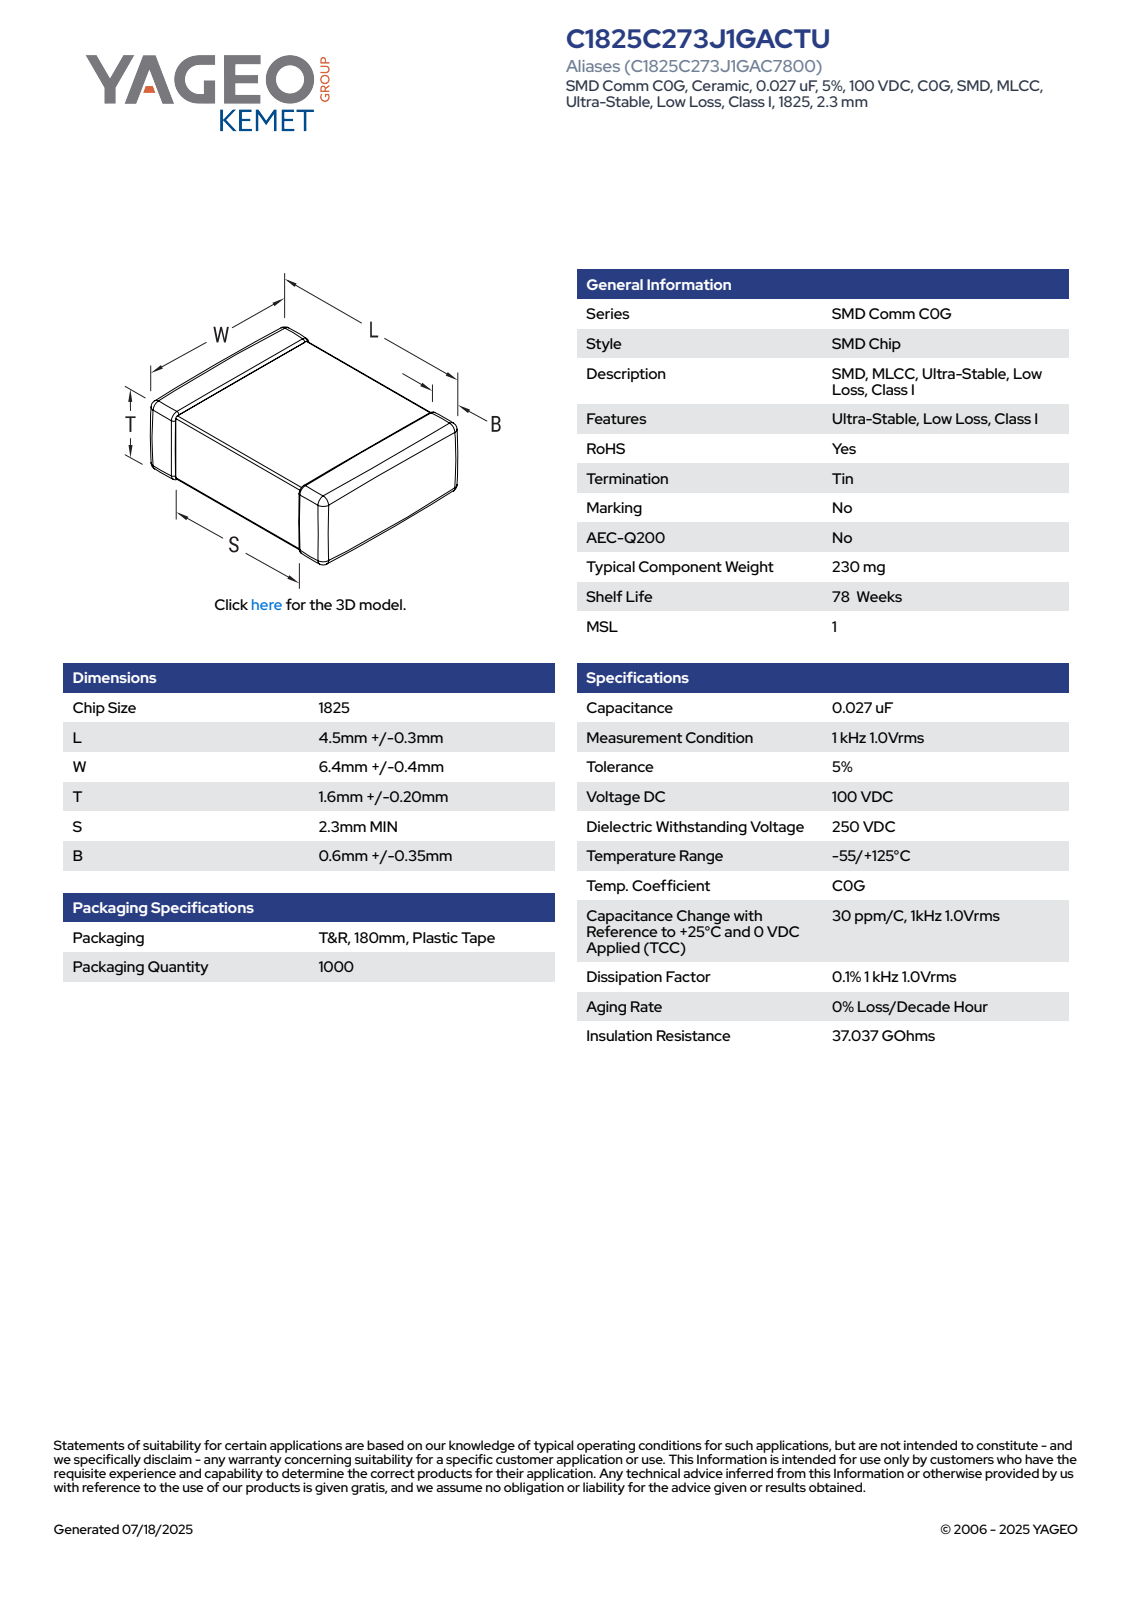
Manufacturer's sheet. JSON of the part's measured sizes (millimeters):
{"part_name": "CCS_CCSTD_1825_L4.8W6.8T1.8B0.6", "step_written_by": "SolidWorks 2021 (AUTOMOTIVE_DESIGN)", "units": "millimeters", "bodies": {"solids": 4, "faces": 125, "planar": 71, "cylindrical": 38, "other": 16}, "overall_size": [6.8, 4.8, 1.8], "volume_mm3": 52, "surface_area_mm2": 109, "partial_cylinders_radius": [[0.14, 24]], "face_to_face_distances": [1.52, 1.66, 4.8, 1.8, 6.66, 6.52, 6.8, 1.59, 3.21, 2.59]}
